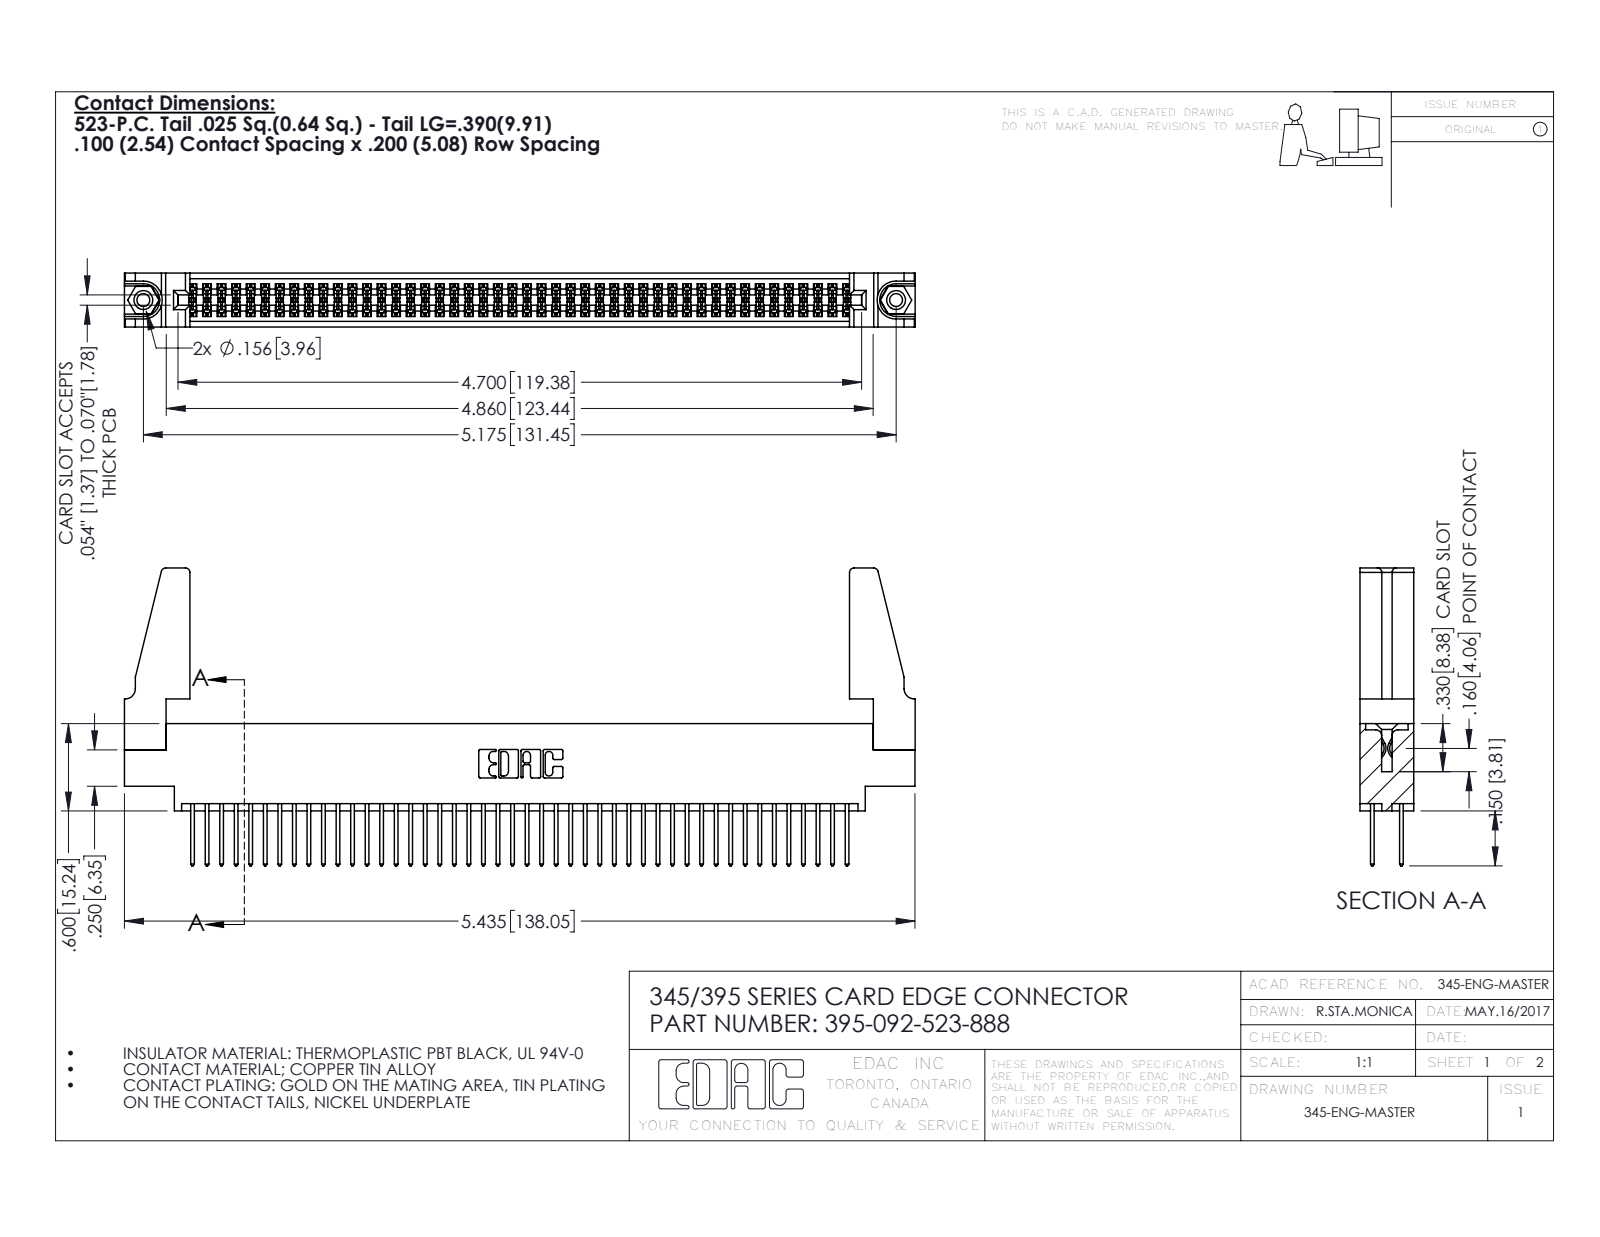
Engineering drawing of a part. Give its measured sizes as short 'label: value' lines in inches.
name: 395-092-523-888; 345-220-078_345-220-088; 345-250-001_345-250-001-102; 345 Part_0.170 Offset - 0.156 Dia-TH (+1 more)
written by: SolidWorks 2016 (CONFIG_CONTROL_DESIGN)
unit: in
bodies: 97 solids, 4854 faces (3192 planar, 1646 cylindrical, 16 other)
size: 5.436 × 2.047 × 0.37
volume: 1.024 in³; area: 37.48 in²
holes: 2× ⌀0.089, 2× ⌀0.125, 2× ⌀0.156, 1× ⌀0.064
bosses: 2× ⌀0.155
rounds: 138× R0.006, 92× R0.01, 22× R0.01, 8× R0.03, 6× R0.007, 6× R0.031, 3× R0.026, 2× R0.014
face distances: 0.072, 0.298, 0.37, 0.2, 0.098, 0.272, 0.025, 0.225, 0.175, 0.149
hole spacings: 0.27, 4.939, 5.175
